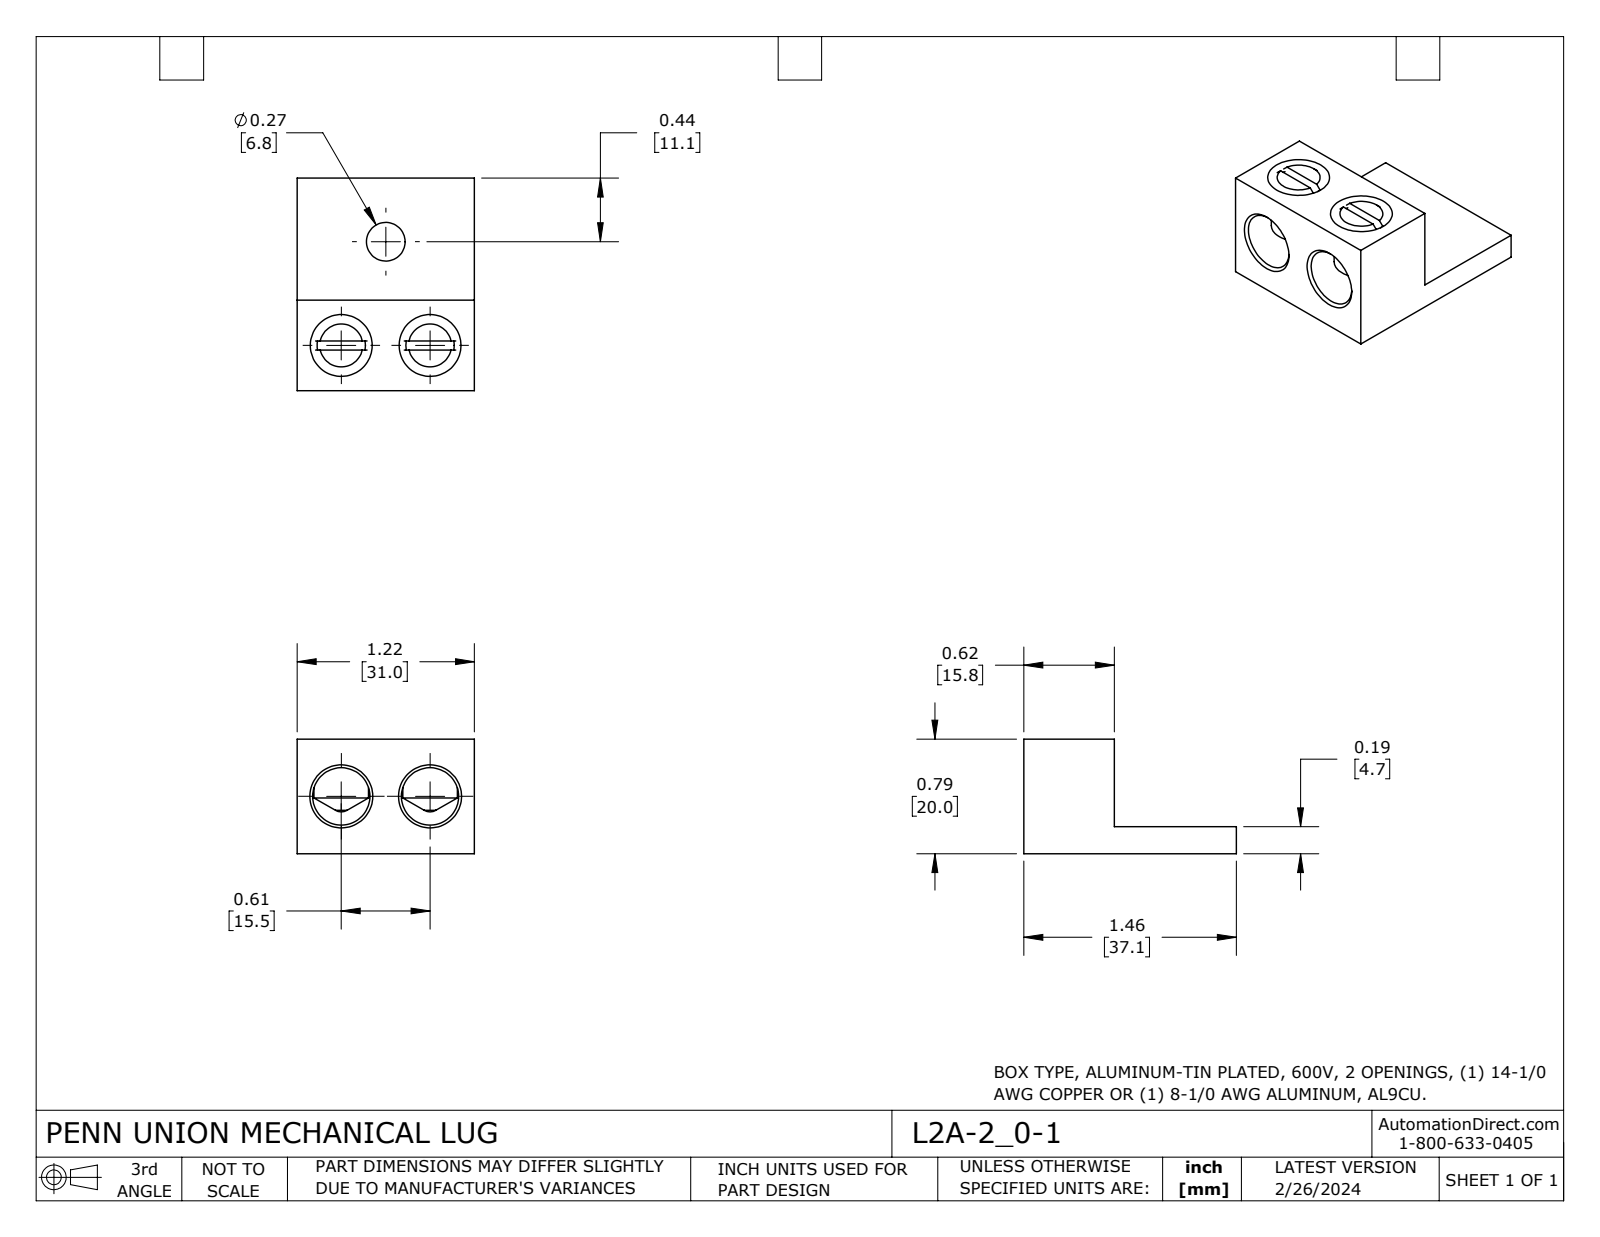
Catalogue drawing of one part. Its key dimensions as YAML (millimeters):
part_name: "L2A-2_0-1"
step_written_by: "SolidWorks 2023 (CONFIG_CONTROL_DESIGN)"
units: millimeters
bodies: {solids: 3, faces: 50, planar: 18, cylindrical: 14, other: 18}
overall_size: [37.1, 31, 20]
volume: 11100
surface_area: 6060
round_holes:
  - {diameter: 8.4, count: 2}
  - {diameter: 10, count: 2}
  - {diameter: 6.8, count: 1}
round_bosses_or_shafts:
  - {diameter: 9.5, count: 2}
face_to_face_distances: [4.7, 30.9, 20, 15.3, 15.8, 37.1, 21.3, 7.1, 8.7, 28.4]
hole_center_spacings: [15.5, 19.7, 19.7]
